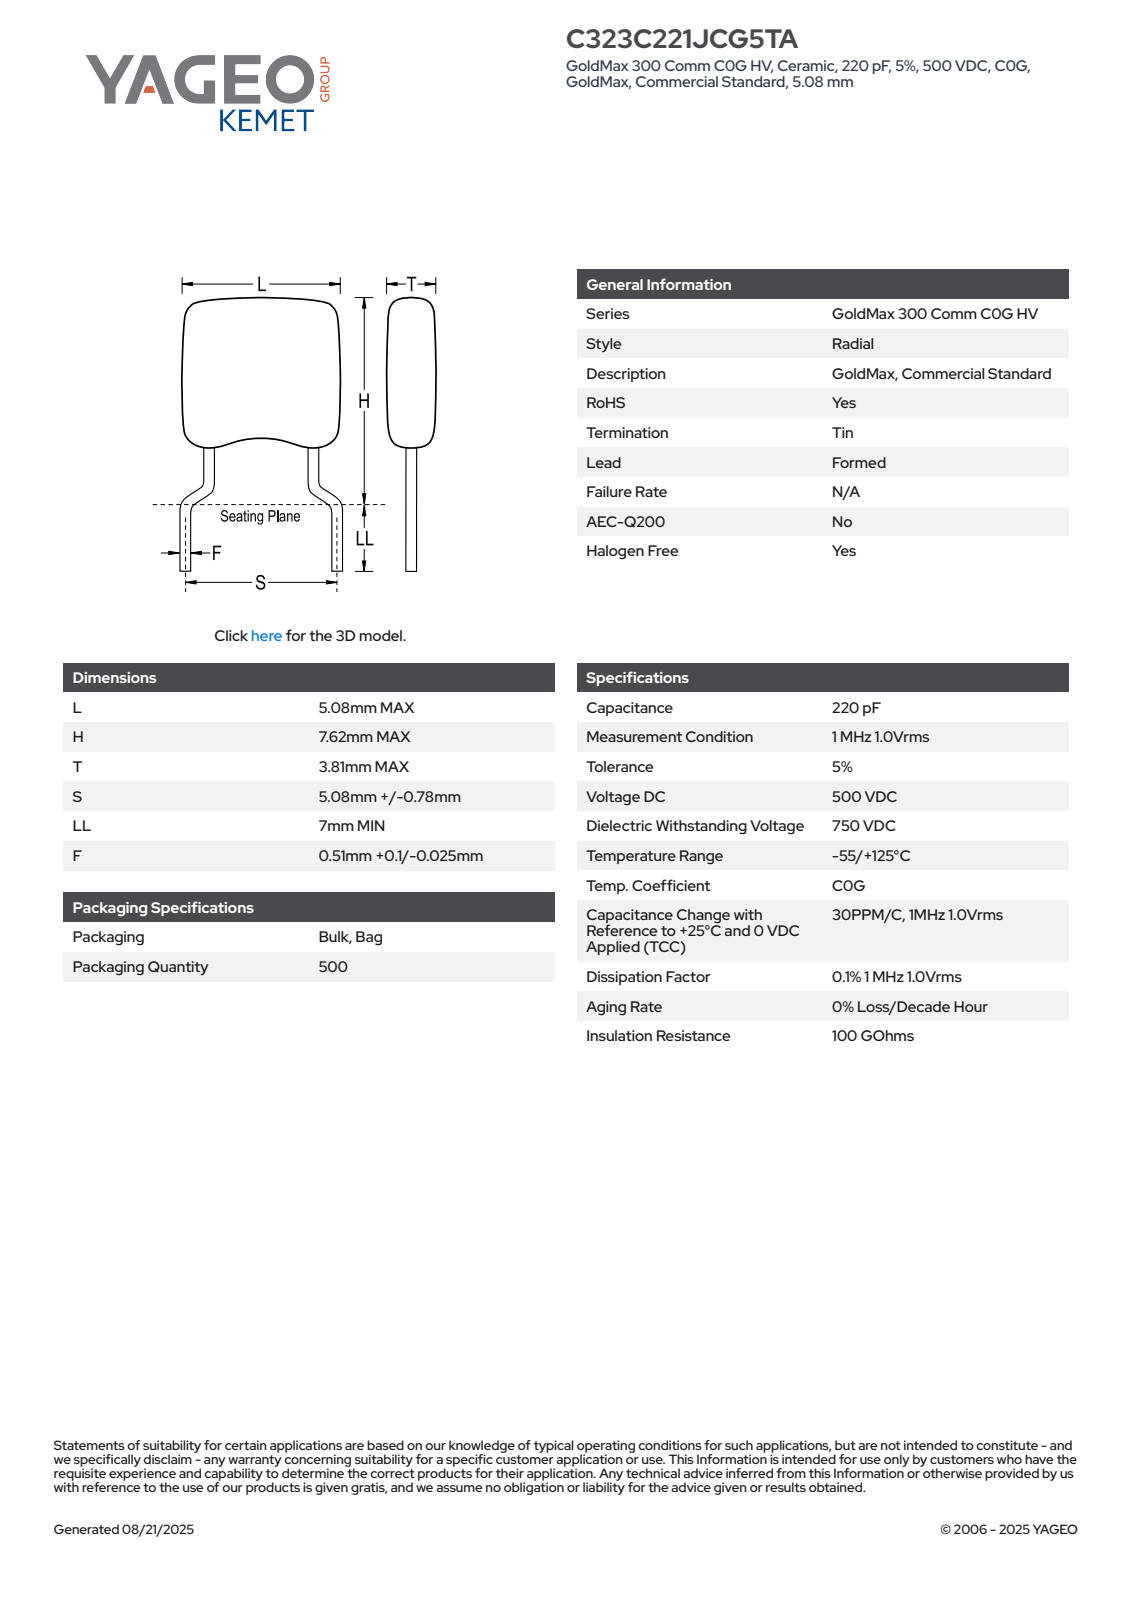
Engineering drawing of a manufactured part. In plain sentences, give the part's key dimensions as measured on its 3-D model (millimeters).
The part is named "CCRC323_L5.08H7.62T3.81S5.08LL7F0.61". Its 3-D file was written by "SolidWorks 2014 (AUTOMOTIVE_DESIGN)". It is 4 solids with 109 faces: 68 planar, 22 cylindrical and 19 other. Overall it measures 14.62 by 5.69 by 3.81 millimeters. Its volume is 91 cubic millimeters and its surface area 146 square millimeters. Round bosses or shafts: 6 of diameter 0.61. Partial cylindrical surfaces (rounded edges, fillets, slot ends): 8 of radius 0.75, 2 of radius 1. The main face-to-face distances are 3.81, 5.08, 4.81, 9.81, 14.62, 0.43, 12.45, 2.64, 2.17, 12.02.
